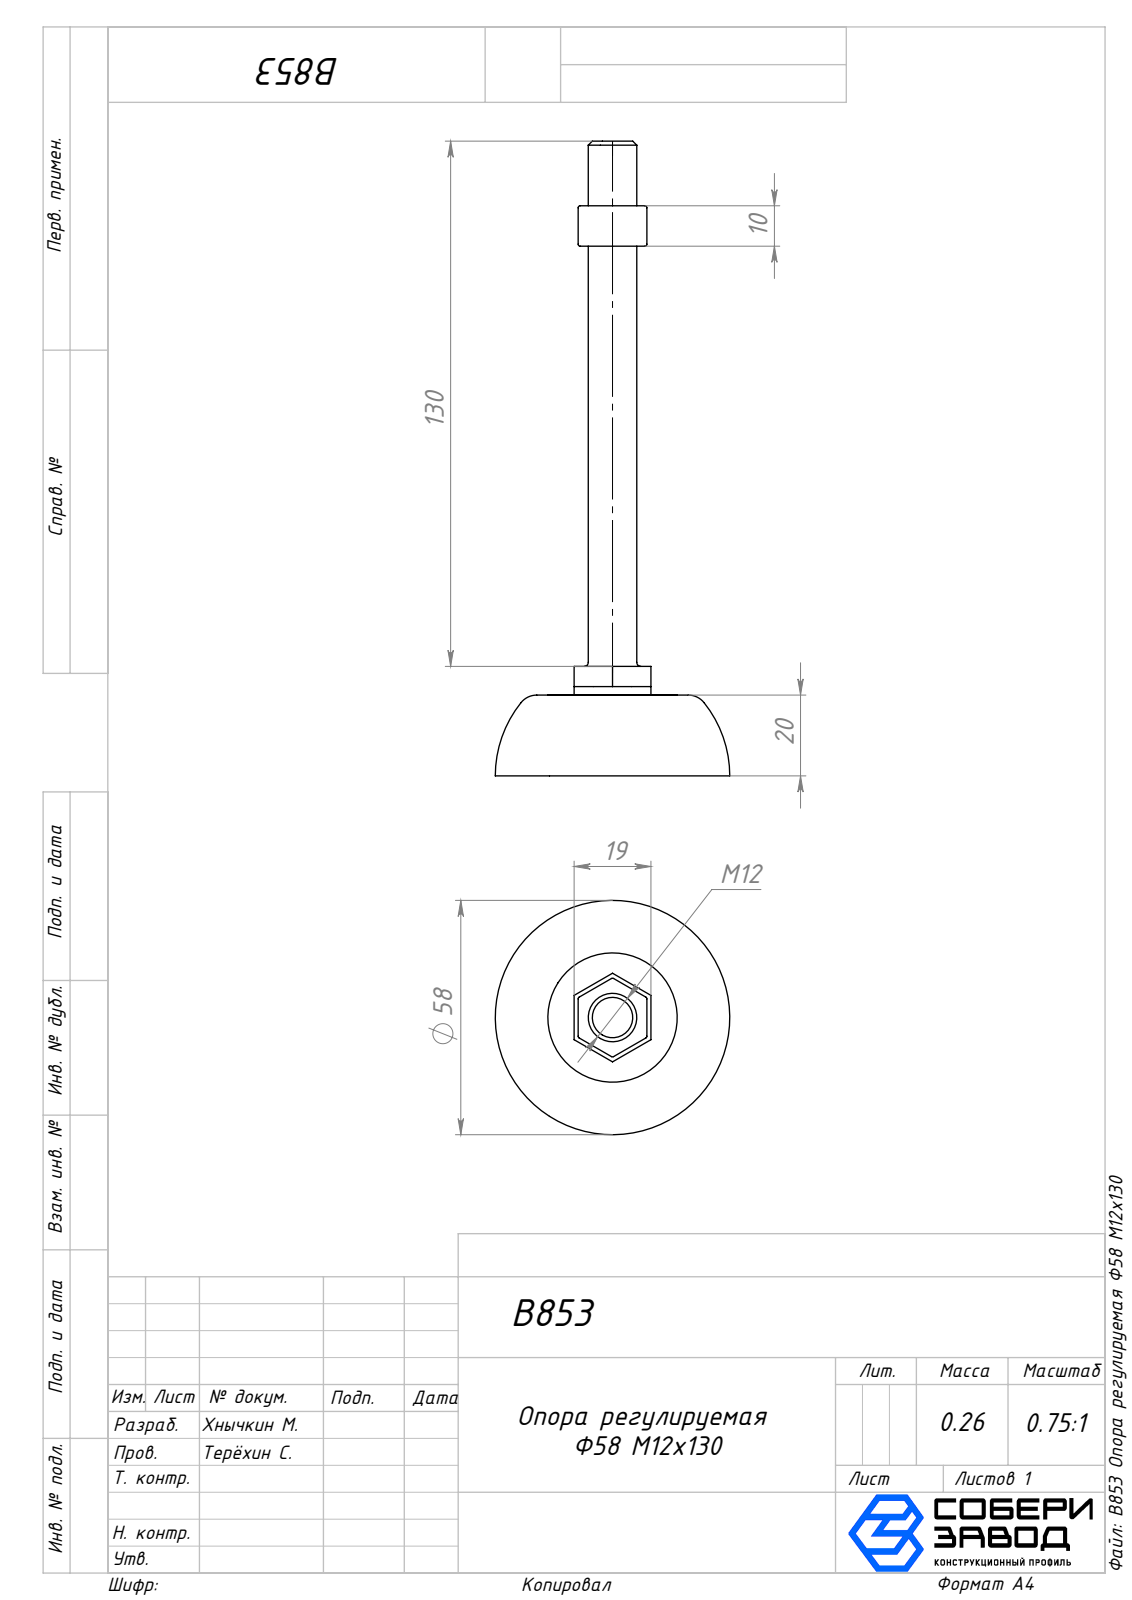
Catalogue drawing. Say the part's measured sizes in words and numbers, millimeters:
The part is named "Вал_00; Мал. гайка_00; B853 Опора регулируемая Ф58 М12х130; Опора_00 (+1 more)". Its 3-D file was written by "SolidWorks 2025 (AUTOMOTIVE_DESIGN)". It is 4 solids with 128 faces: 36 planar, 50 cylindrical and 42 other. Overall it measures 157.1 by 58 by 58 millimeters. Its volume is 32 891 cubic millimeters and its surface area 17 070 square millimeters. Round holes: 1 of diameter 4, 1 of diameter 5, 1 of diameter 8. Round bosses or shafts: 1 of diameter 32, 1 of diameter 19, 1 of diameter 12. Partial cylindrical surfaces (rounded edges, fillets, slot ends): 36 of radius 0.5. The main face-to-face distances are 19.9, 20.1, 1, 18, 20, 17, 10, 19, 27.1, 7.2.
